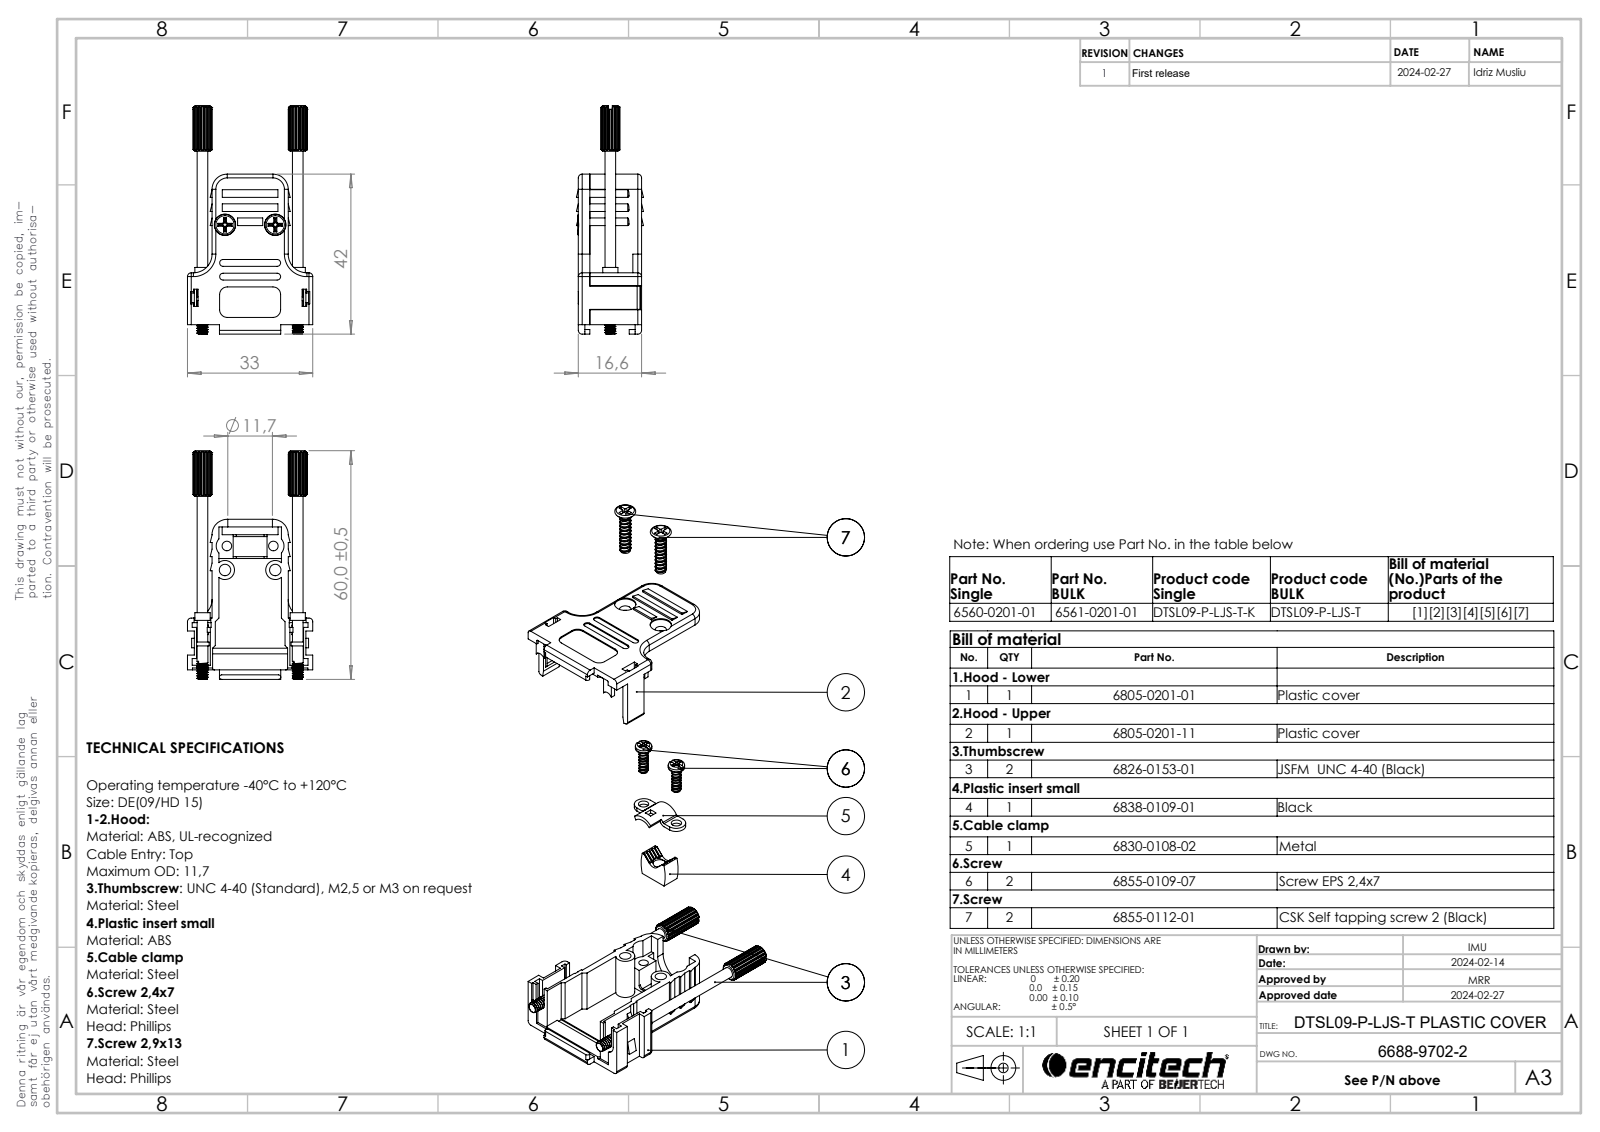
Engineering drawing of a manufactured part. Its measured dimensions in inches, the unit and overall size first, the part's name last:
Units: inches
Overall size (bounding box): 2.362 × 1.295 × 0.693
Round holes (diameter × count): ⌀0.098 ×2, ⌀0.106 ×2, ⌀0.118 ×2, ⌀0.22 ×2, ⌀0.138 ×1
Round bosses / shafts (diameter × count): ⌀0.169 ×2, ⌀0.157 ×2, ⌀0.138 ×2, ⌀0.112 ×2, ⌀0.11 ×2, ⌀0.097 ×2, ⌀0.08 ×2
Partial cylindrical surfaces — rounded edges, fillets, slot ends (radius × count): R0.039 ×16, R0.014 ×9, R0.079 ×5, R0.02 ×4, R0.035 ×4, R0.059 ×4, R0.098 ×4, R0.01 ×2
Main face-to-face distances: 0.071, 0.079, 0.575, 0.047, 0.535, 0.654, 0.583, 0.504, 0.97, 0.254
Hole centre spacings: 0.24, 0.249, 0.355, 0.558, 0.48, 0.52
Volume: 0.505 in³ · Surface area: 18.56 in²
Bodies: 10 solids, 931 faces (556 planar, 293 cylindrical, 82 other)
Part name (STEP PRODUCT): 6830-0108-02; 6805-0201-11; 6855-0109-07; 6688-9702-2 (+4 more)
STEP written by: SolidWorks 2021 (AUTOMOTIVE_DESIGN)
